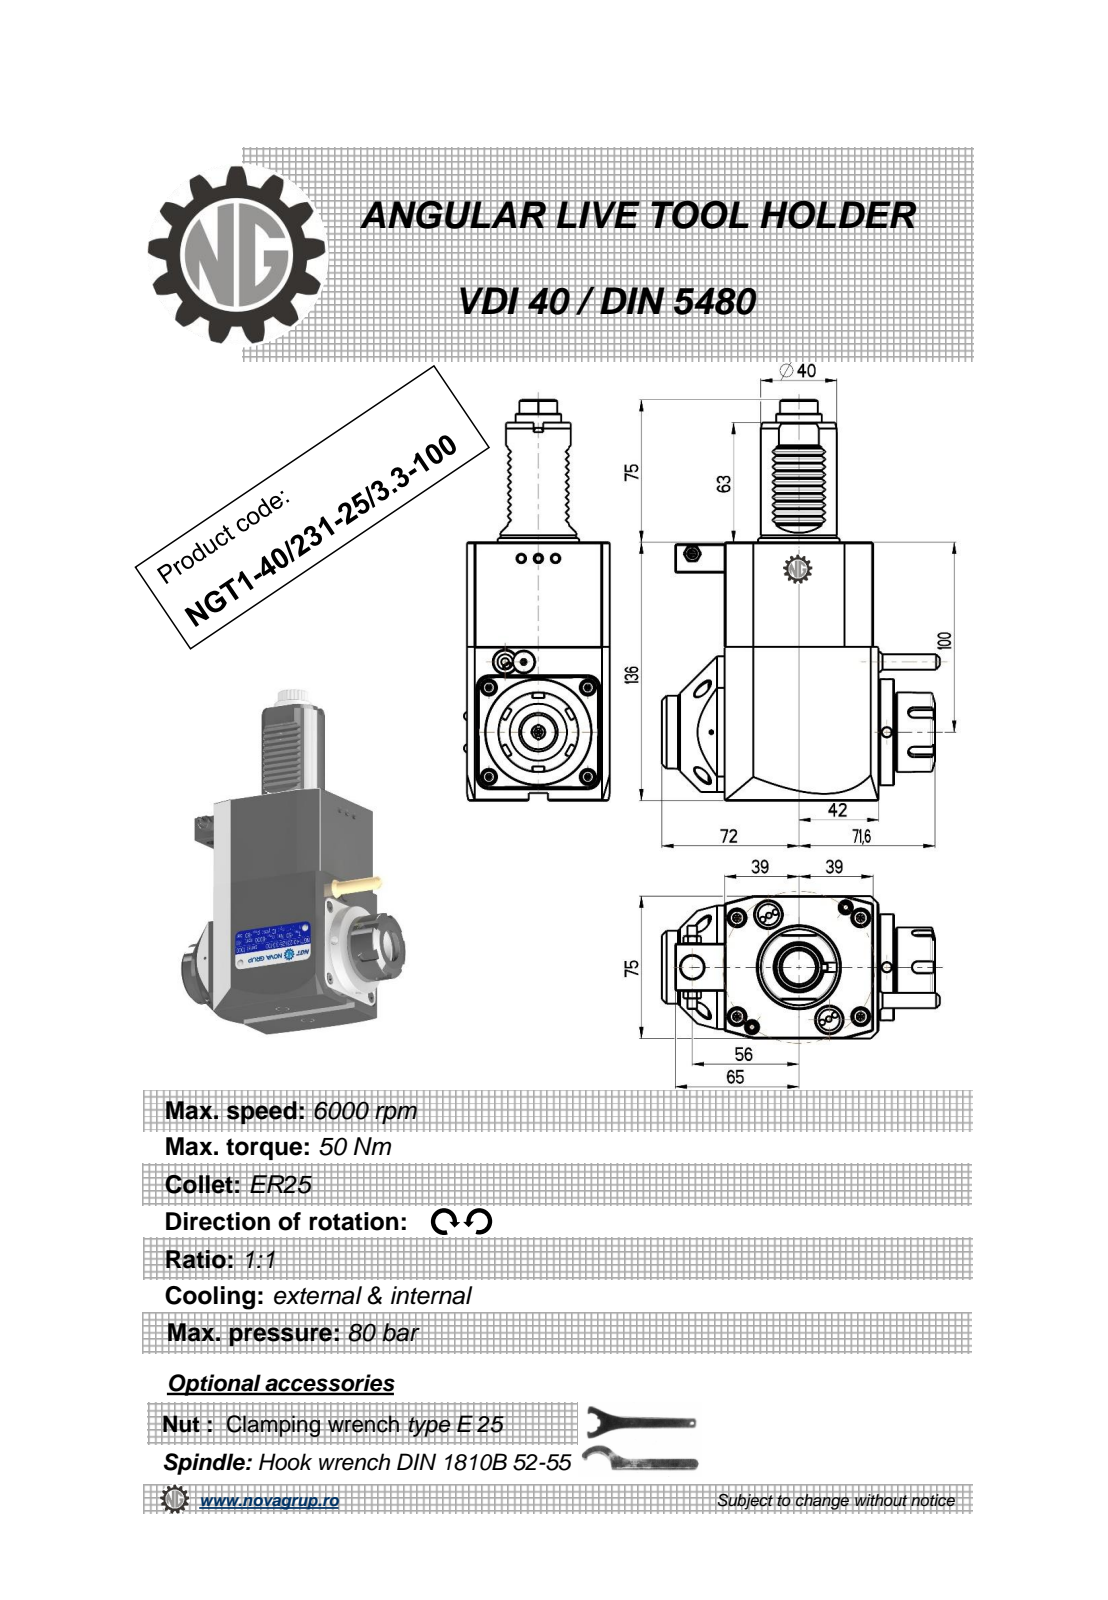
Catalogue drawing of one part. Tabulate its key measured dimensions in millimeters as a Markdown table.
| quantity | value |
| --- | --- |
| part name | NGT1_40_231_25_3_3_100 |
| STEP written by | PRO/ENGINEER BY PARAMETRIC TECHNOLOGY CORPORATION, 2010280 (CONFIG_CONTROL_DESIGN) |
| units | millimeters |
| bodies | 1 solid, 639 faces (229 planar, 233 cylindrical, 177 other) |
| overall size | 211 × 146.14 × 75 |
| volume | 1 008 000 mm³ |
| surface area | 78 195 mm² |
| round holes (diameter × count) | 5 × 3, 3 × 1, 4.2 × 1, 9.5 × 1, 12 × 1, 20.3 × 1 |
| round bosses / shafts (diameter × count) | 56 × 1, 43 × 1, 42 × 1, 40 × 1, 38.5 × 1, 33 × 1, 24 × 1, 11.2 × 1 |
| partial cylindrical surfaces (radius × count) | 2.08 × 48, 0.3 × 20, 0.26 × 12, 0.22 × 6, 3 × 5, 9.08 × 1, 9.92 × 1, 15 × 1 |
| main face-to-face distances | 75, 136, 78, 81, 3, 11, 8, 84.88, 7.5, 8.2 |
| hole center spacings | 40.93, 57.24, 91.5, 102.25, 138.89 |
